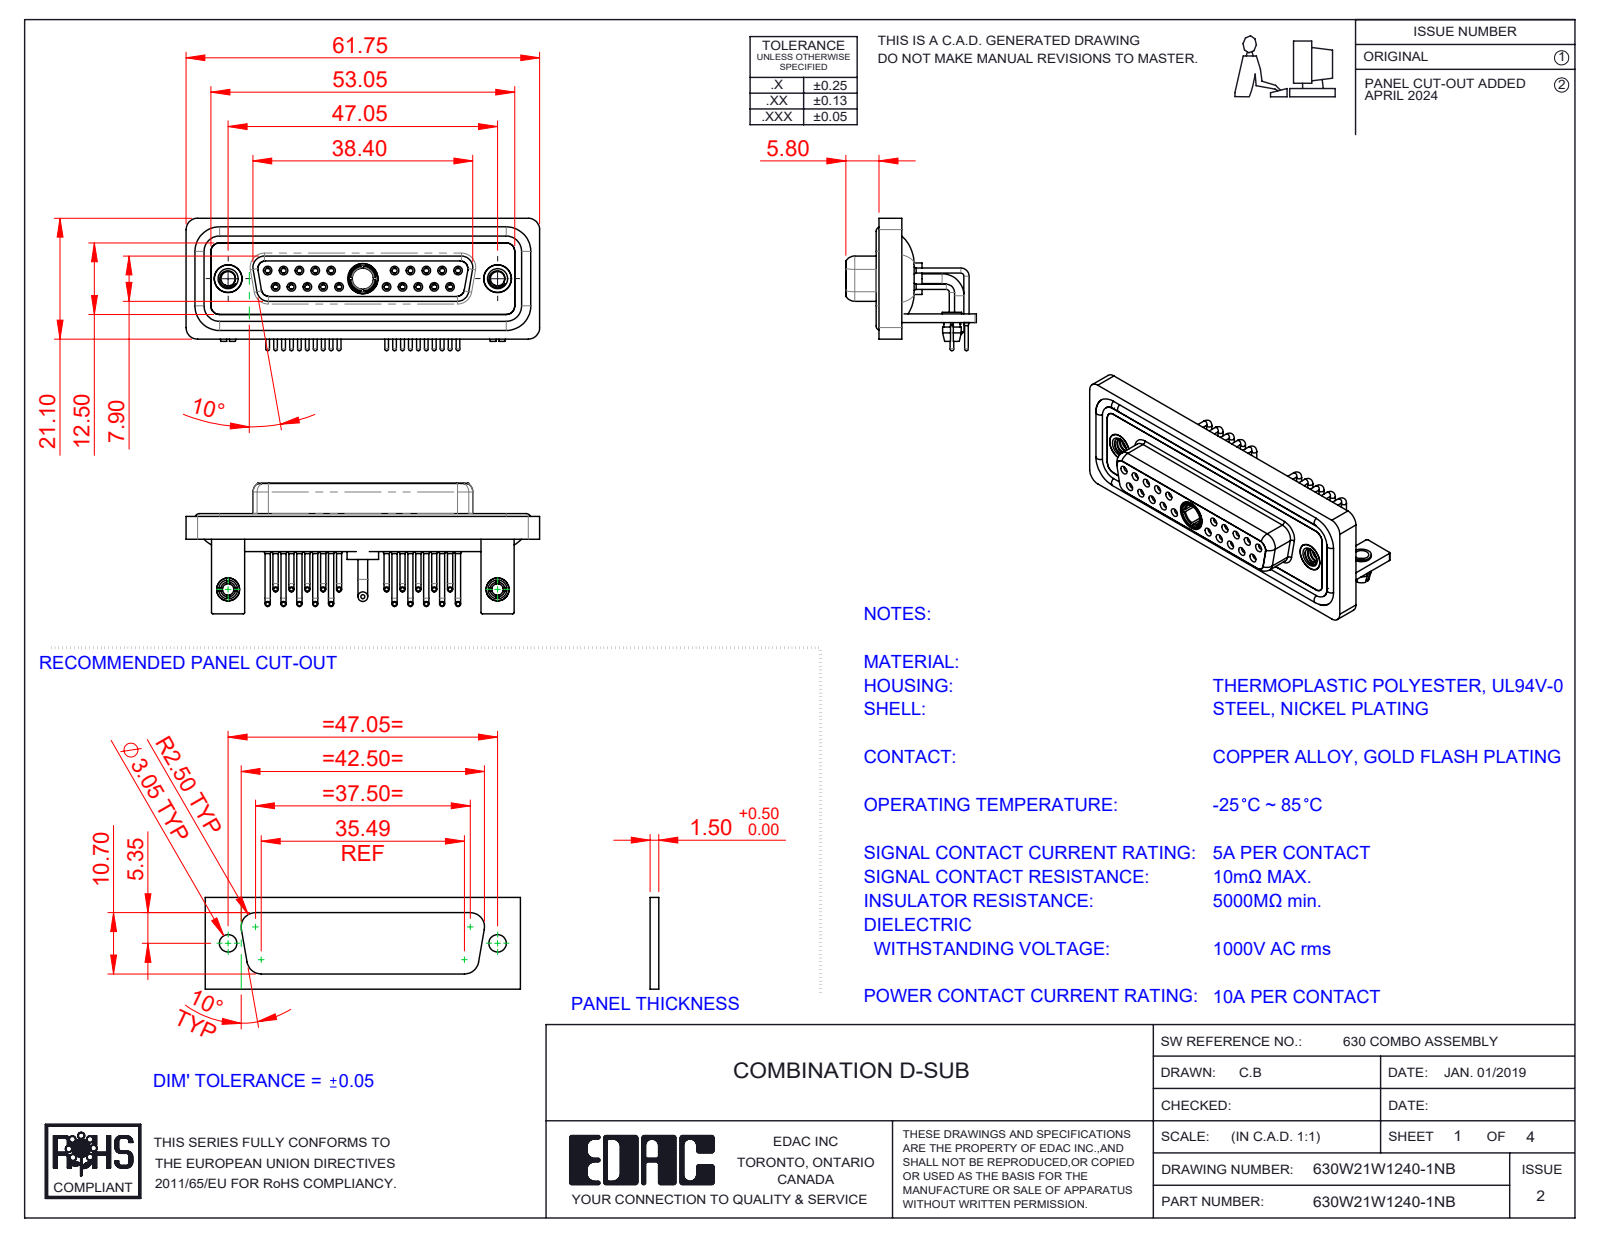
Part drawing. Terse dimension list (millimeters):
name: 630Combo Contact Row 1_50 Contacts; 630Combo Waterproof Housing_25 Contacts; 630Combo Board Lock_50 Contacts; 630Combo Threaded Rivet_A (+7 more)
written by: SolidWorks 2023 (CONFIG_CONTROL_DESIGN)
unit: mm
bodies: 33 solids, 1658 faces (502 planar, 727 cylindrical, 429 other)
size: 61.75 × 23.12 × 22.8
volume: 8 843 mm³; area: 15 678 mm²
holes: 22× ⌀2, 20× ⌀0.9, 20× ⌀1.1, 20× ⌀1.5, 10× ⌀1.6, 10× ⌀1.7, 4× ⌀2.5, 3× ⌀4.85, 2× ⌀3.2, 2× ⌀4, 2× ⌀4.05, 2× ⌀5
bosses: 20× ⌀0.9, 20× ⌀0.65, 14× ⌀1.6, 2× ⌀4.95, 2× ⌀4.8, 2× ⌀4, 2× ⌀3.4, 2× ⌀3.3
rounds: 19× R2, 18× R1.5, 16× R0.25, 8× R1.35, 8× R1.6, 5× R0.5, 4× R0.6, 4× R0.65
face distances: 0.4, 1.8, 2.9, 3.7, 1.5, 4.1, 1.1, 1.4, 1.6, 2.5
hole spacings: 3.16, 2.77, 5.54, 8.31, 5.04, 19.39, 20.97, 22.16
